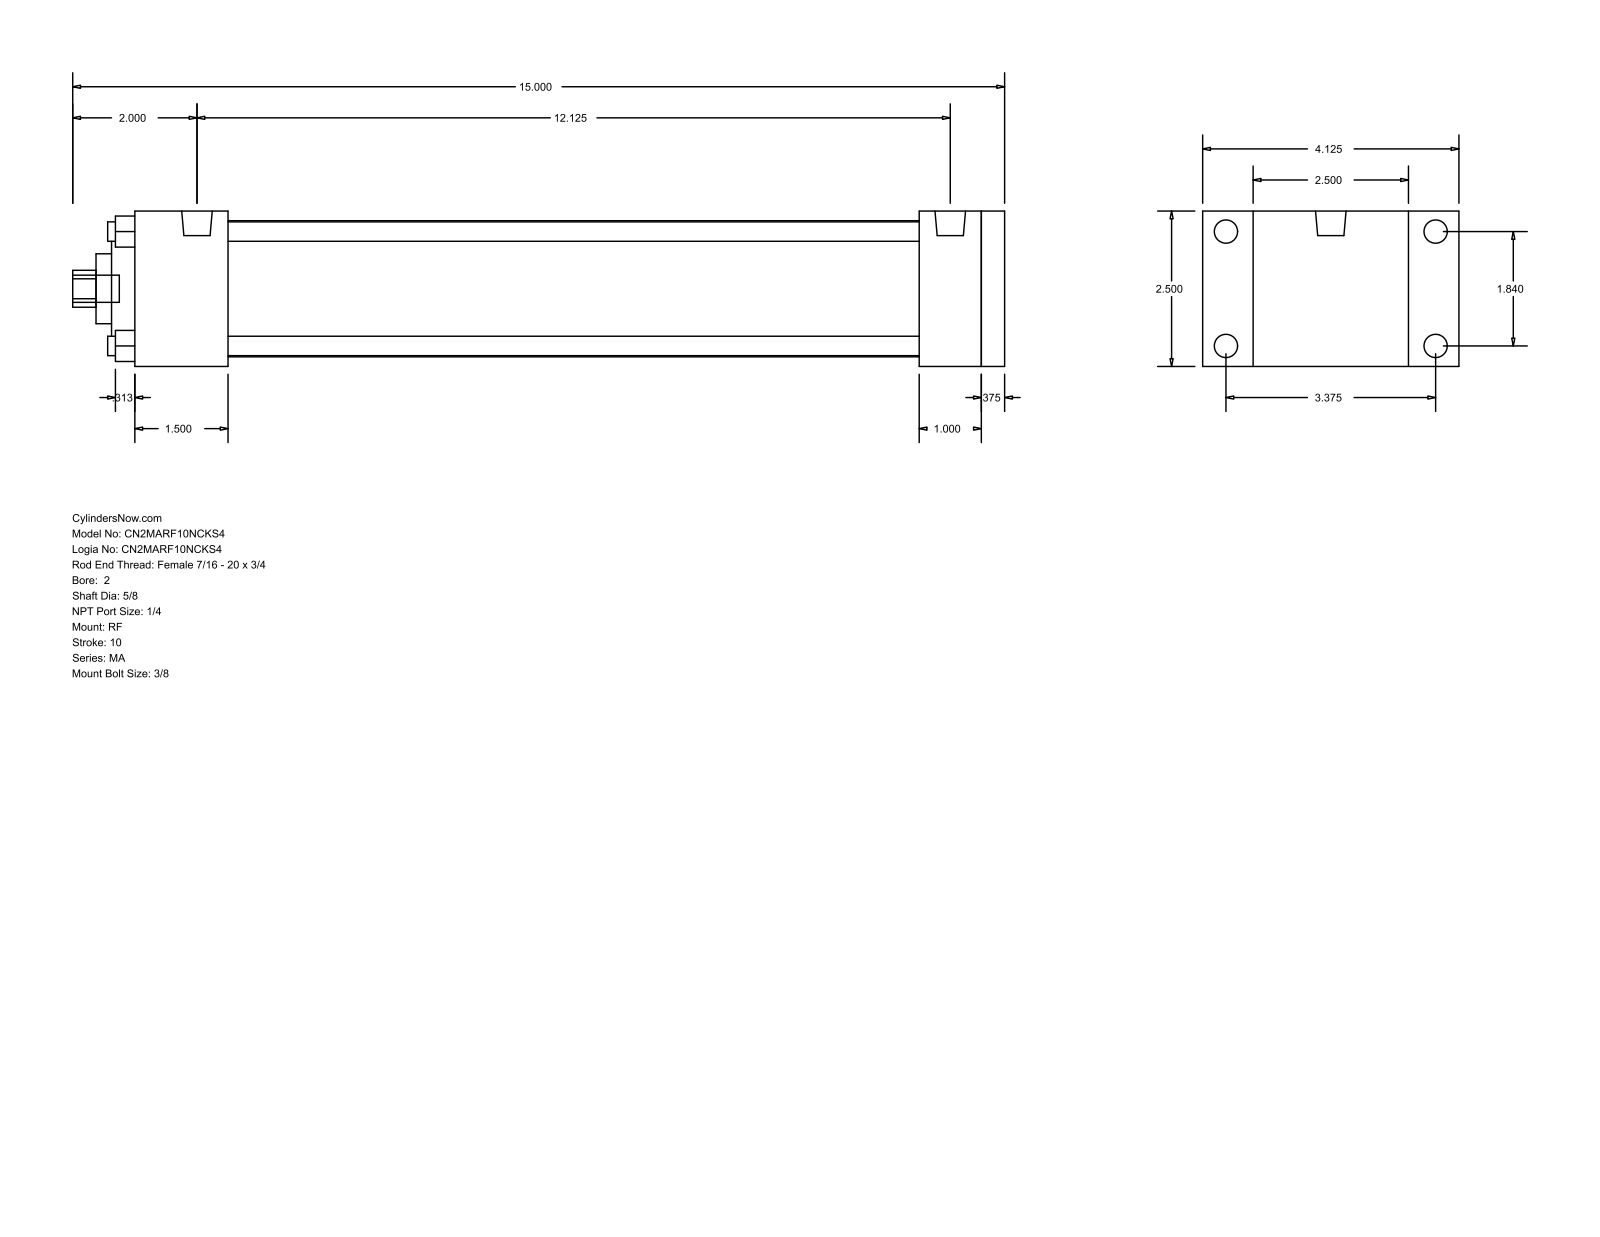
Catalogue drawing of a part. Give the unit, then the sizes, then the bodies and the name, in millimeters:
Units: millimetres
Overall size (bounding box): 381 × 104.78 × 63.5
Round holes (diameter × count): ⌀7.94 ×4, ⌀15.88 ×1, ⌀28.57 ×1, ⌀50.8 ×1, ⌀55.63 ×1
Round bosses / shafts (diameter × count): ⌀9.53 ×4, ⌀7.94 ×4, ⌀12.49 ×2, ⌀11.11 ×1
Partial cylindrical surfaces — rounded edges, fillets, slot ends (radius × count): R7.54 ×1
Main face-to-face distances: 63.5, 9.52, 355.6, 38.1, 346.08, 307.98, 317.5, 320.67, 282.57, 25.41
Hole centre spacings: 33.05, 46.74, 66.1
Bodies: 0 solids, 94 faces (65 planar, 29 cylindrical, 0 other)
Part name (STEP PRODUCT): MA_RF__0200_0.625
STEP written by: GSSL Pune (CONFIG_CONTROL_DESIGN)
